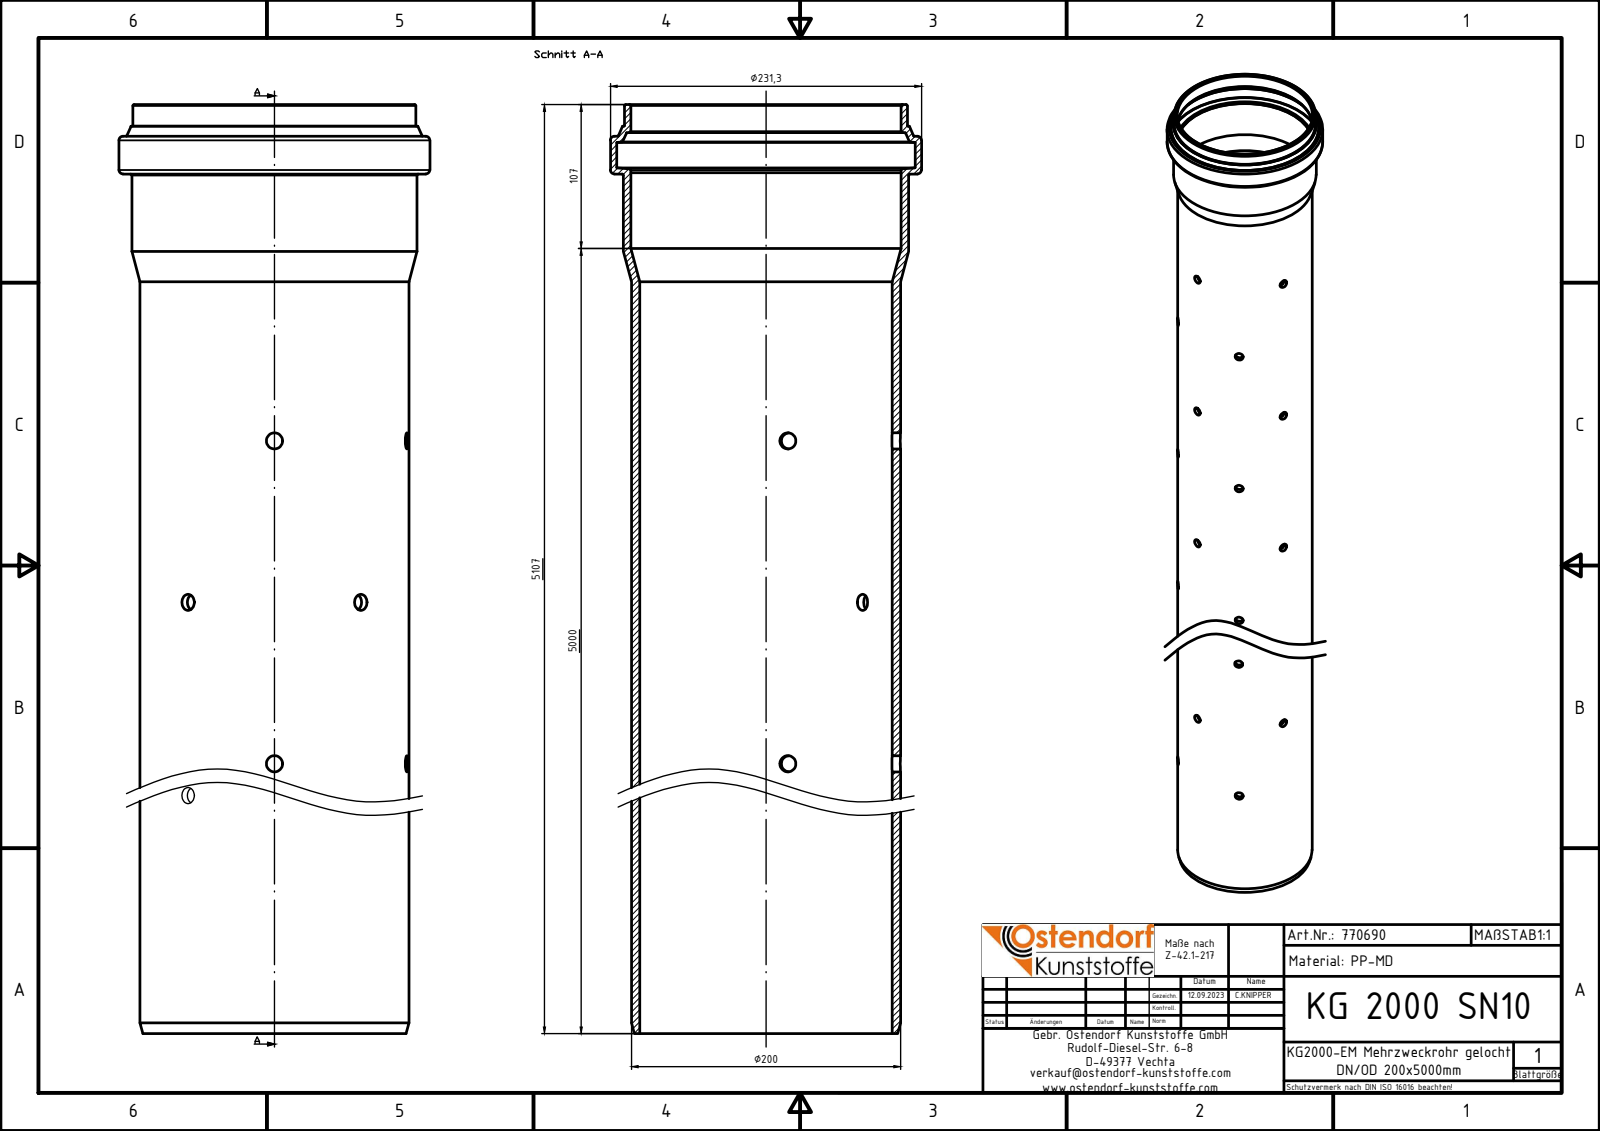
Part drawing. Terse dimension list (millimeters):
name: 770690z
written by: Autodesk Inventor 2024 (AUTOMOTIVE_DESIGN)
unit: mm
bodies: 1 solid, 117 faces (6 planar, 89 cylindrical, 22 other)
size: 5107 × 231.3 × 231.3
volume: 19 230 000 mm³; area: 6 259 000 mm²
holes: 80× ⌀12, 1× ⌀187.6, 1× ⌀200.8, 1× ⌀201, 1× ⌀221.9
bosses: 1× ⌀231.3, 1× ⌀212, 1× ⌀210.4, 1× ⌀200
face distances: 5055.3, 5083.5, 28.2, 5107, 51.7, 23.5, 5090.97, 35.67, 7.47, 16.03
hole spacings: 240, 480, 720, 960, 1200, 1440, 1680, 1920
